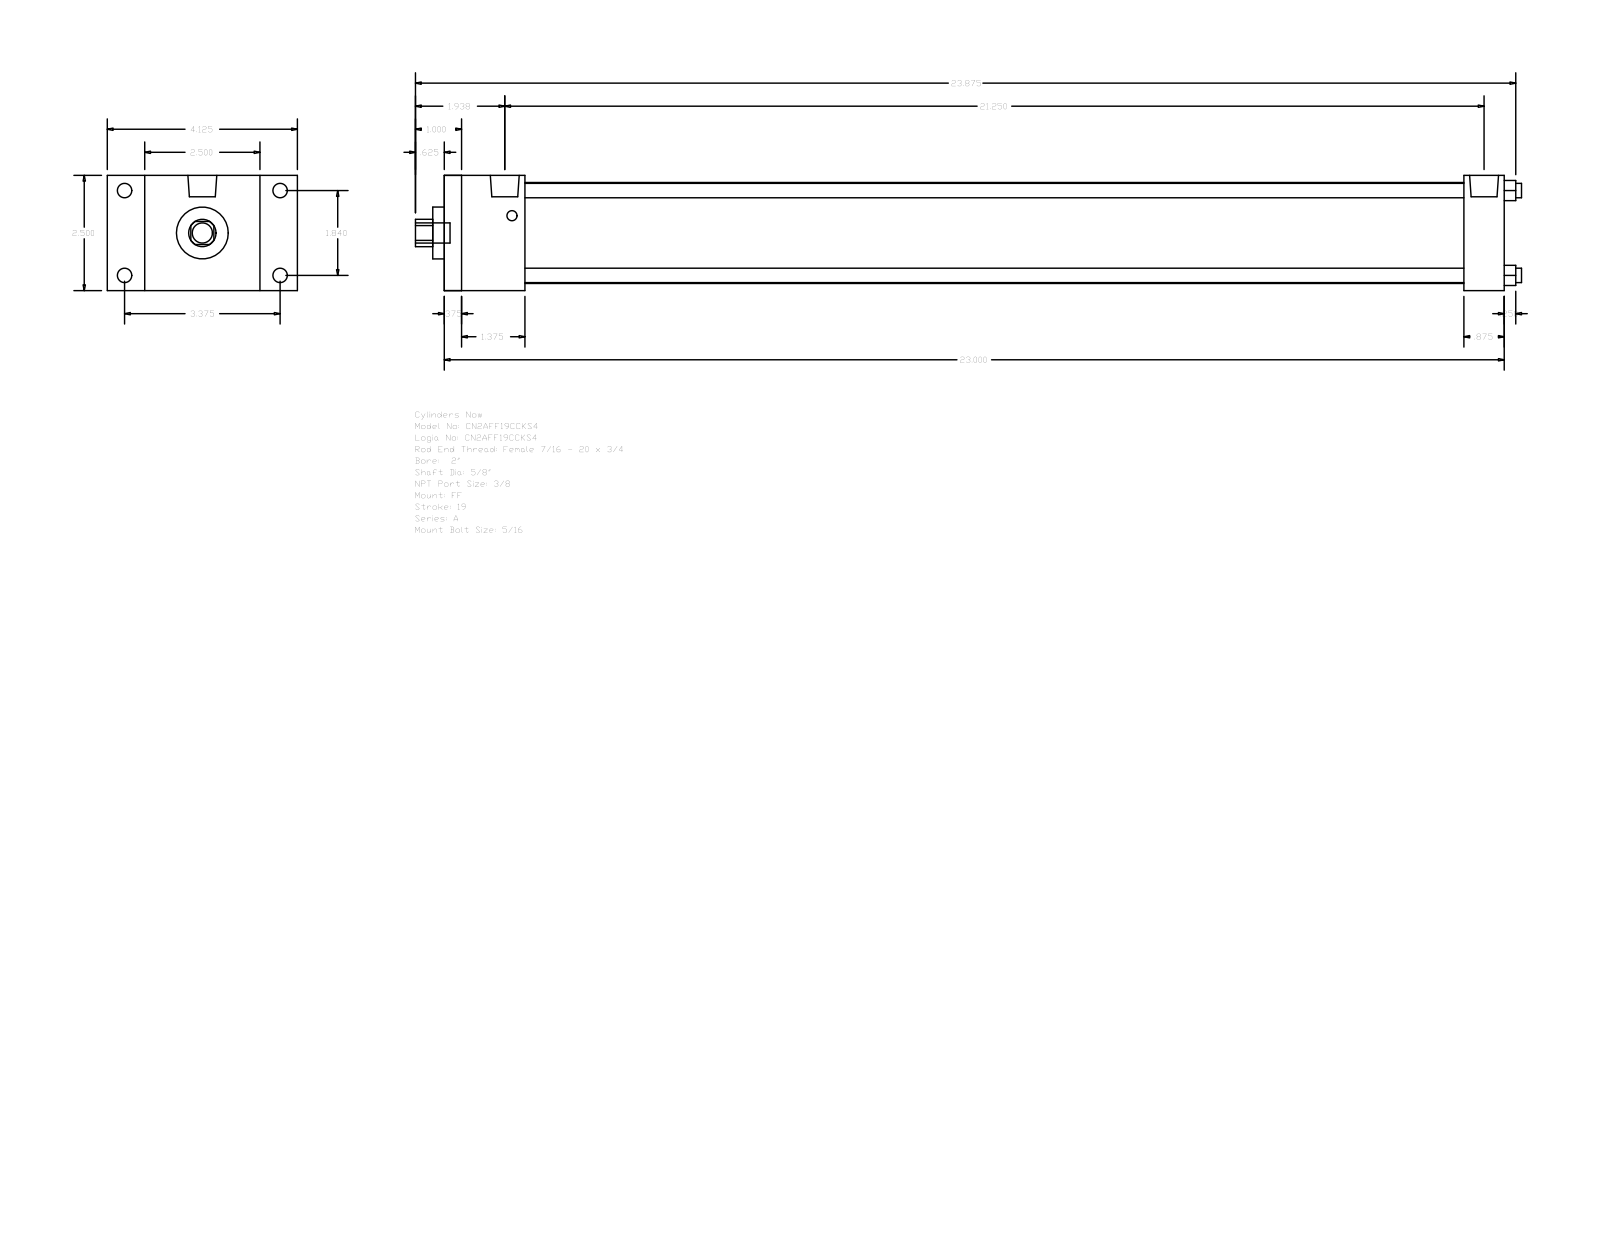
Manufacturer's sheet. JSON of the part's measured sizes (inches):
{"part_name": "A_FF__0200_0.625", "step_written_by": "GSSL Pune (CONFIG_CONTROL_DESIGN)", "units": "inches", "bodies": {"solids": 0, "faces": 92, "planar": 64, "cylindrical": 28, "other": 0}, "overall_size": [24, 4.125, 2.5], "round_holes": [[0.313, 4], [0.625, 1], [1.125, 1], [2.19, 1]], "round_bosses_or_shafts": [[0.313, 4], [0.219, 4], [0.627, 2], [0.437, 1]], "partial_cylinders_radius": [[0.297, 1]], "face_to_face_distances": [2.5, 23, 0.375, 22.625, 1.75, 22.125, 1.375, 21.75, 20.375, 21.25], "hole_center_spacings": [1.301, 1.84, 2.602]}
